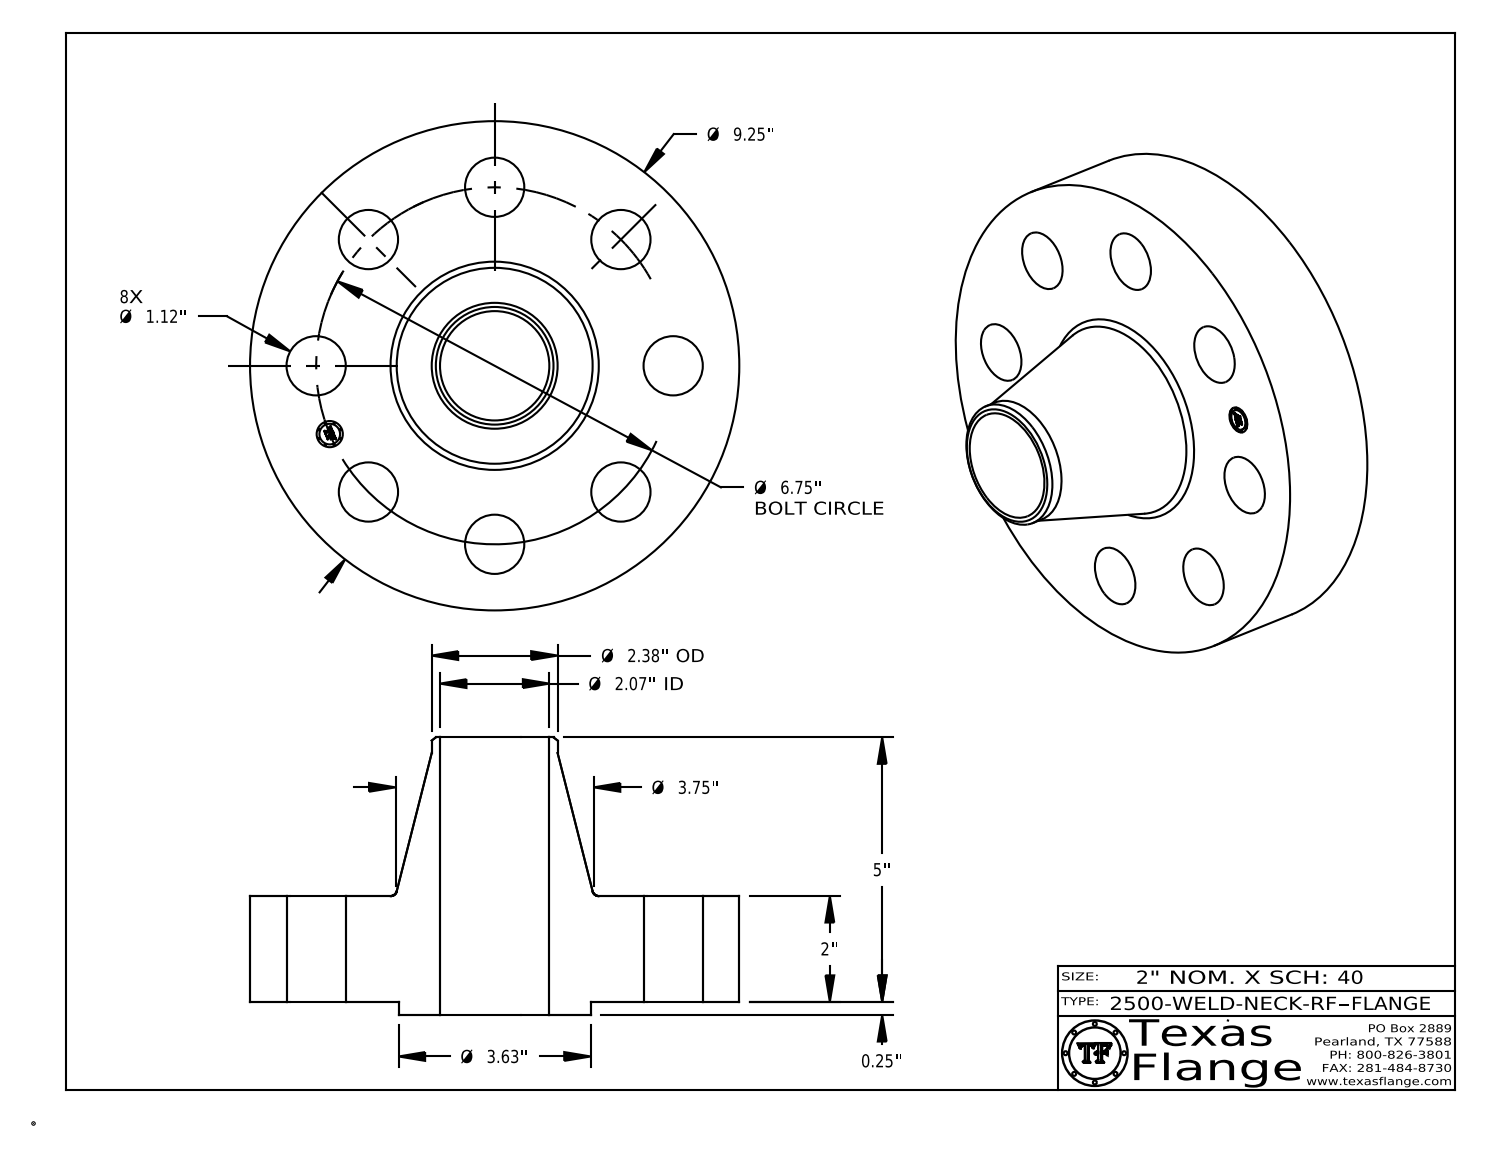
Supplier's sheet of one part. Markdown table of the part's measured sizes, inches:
| quantity | value |
| --- | --- |
| part name | 2500-WELD-NECK-RF |
| STEP written by | CATIA V5 STEP AP214 (AUTOMOTIVE_DESIGN) |
| units | inches |
| bodies | 1 solid, 419 faces (369 planar, 44 cylindrical, 6 other) |
| overall size | 9.25 × 9.25 × 5.25 |
| volume | 125.2 in³ |
| surface area | 285.2 in² |
| round holes (diameter × count) | 1.12 × 8, 0.495 × 1, 2.067 × 1 |
| round bosses / shafts (diameter × count) | 0.03 × 8, 9.25 × 1, 3.63 × 1, 2.38 × 1, 0.39 × 1 |
| main face-to-face distances | 2, 0.25, 2.25, 5.25, 5, 3, 2.235, 1.985, 0.015, 3.015 |
| hole center spacings | 3.375, 2.583, 4.773, 6.237, 6.75, 1.317, 5.613, 6.62 |
